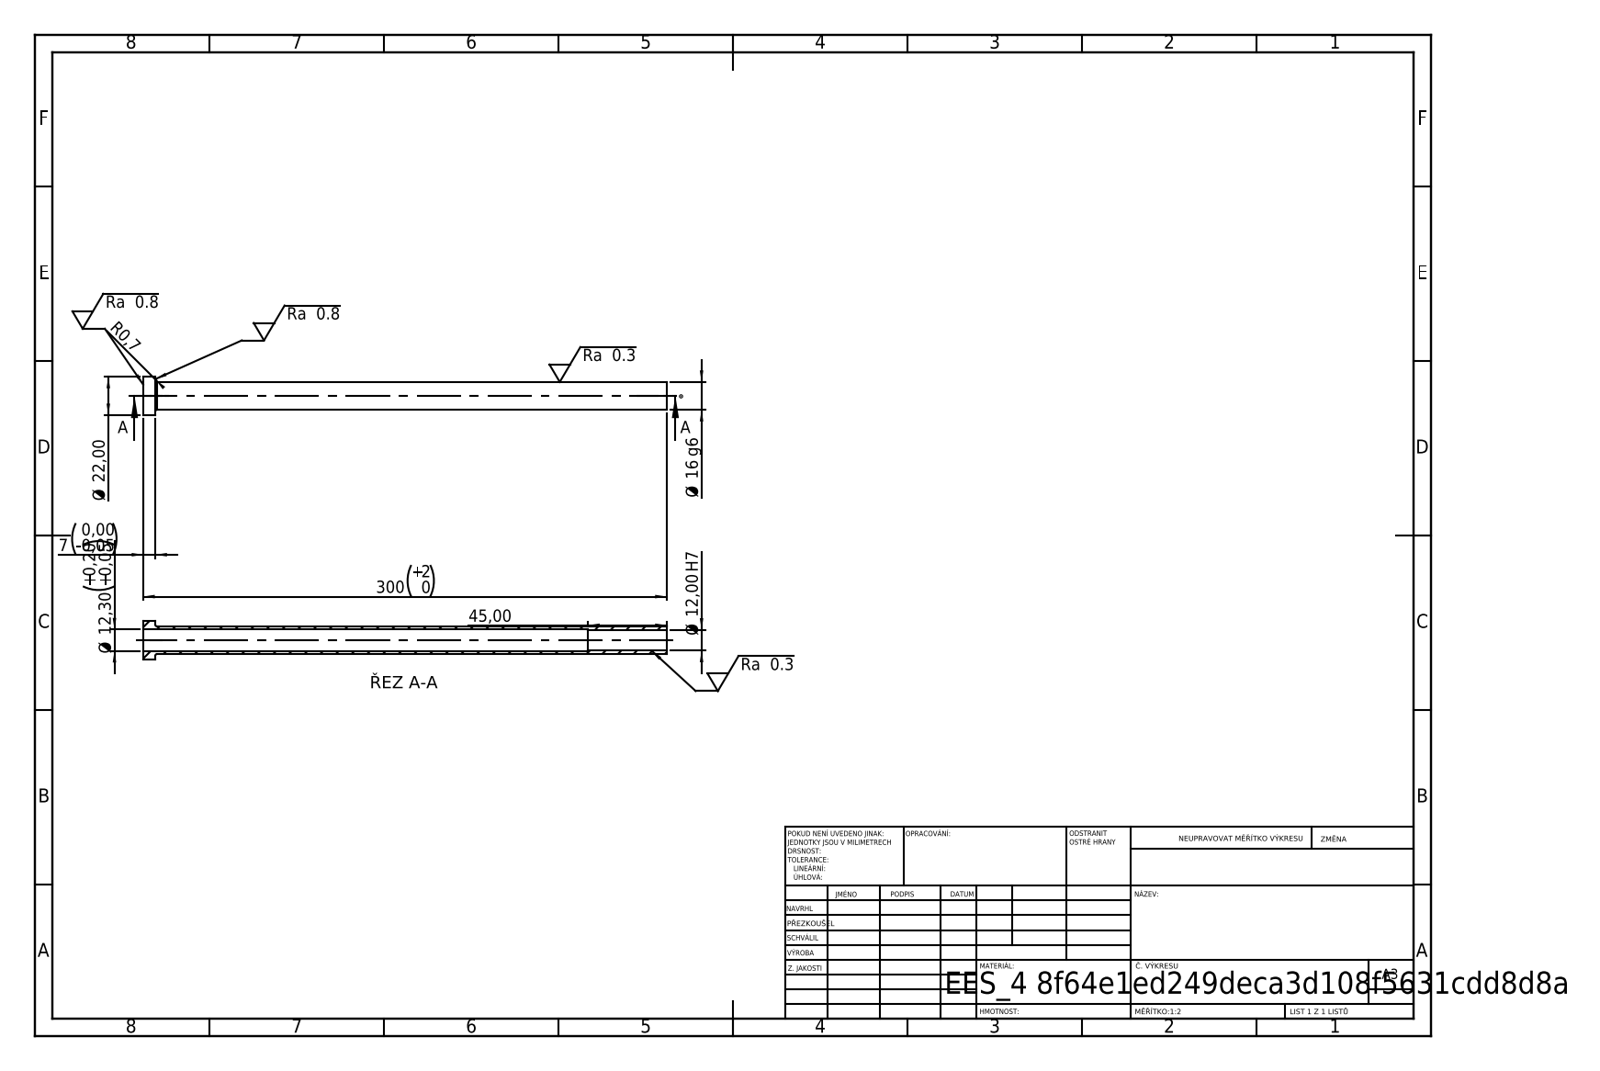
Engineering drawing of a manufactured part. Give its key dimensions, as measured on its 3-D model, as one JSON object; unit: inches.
{"step_written_by": "SolidWorks 2019 (CONFIG_CONTROL_DESIGN)", "units": "inches", "bodies": {"solids": 1, "faces": 14, "planar": 4, "cylindrical": 8, "other": 2}, "overall_size": [11.811, 0.866, 0.866], "volume_in3": 1.598, "surface_area_in2": 42.29, "round_holes": [[0.472, 1], [0.484, 1]], "round_bosses_or_shafts": [[0.866, 1], [0.63, 1]], "face_to_face_distances": [0.276, 11.811, 11.535, 10.039, 9.764, 1.772]}
